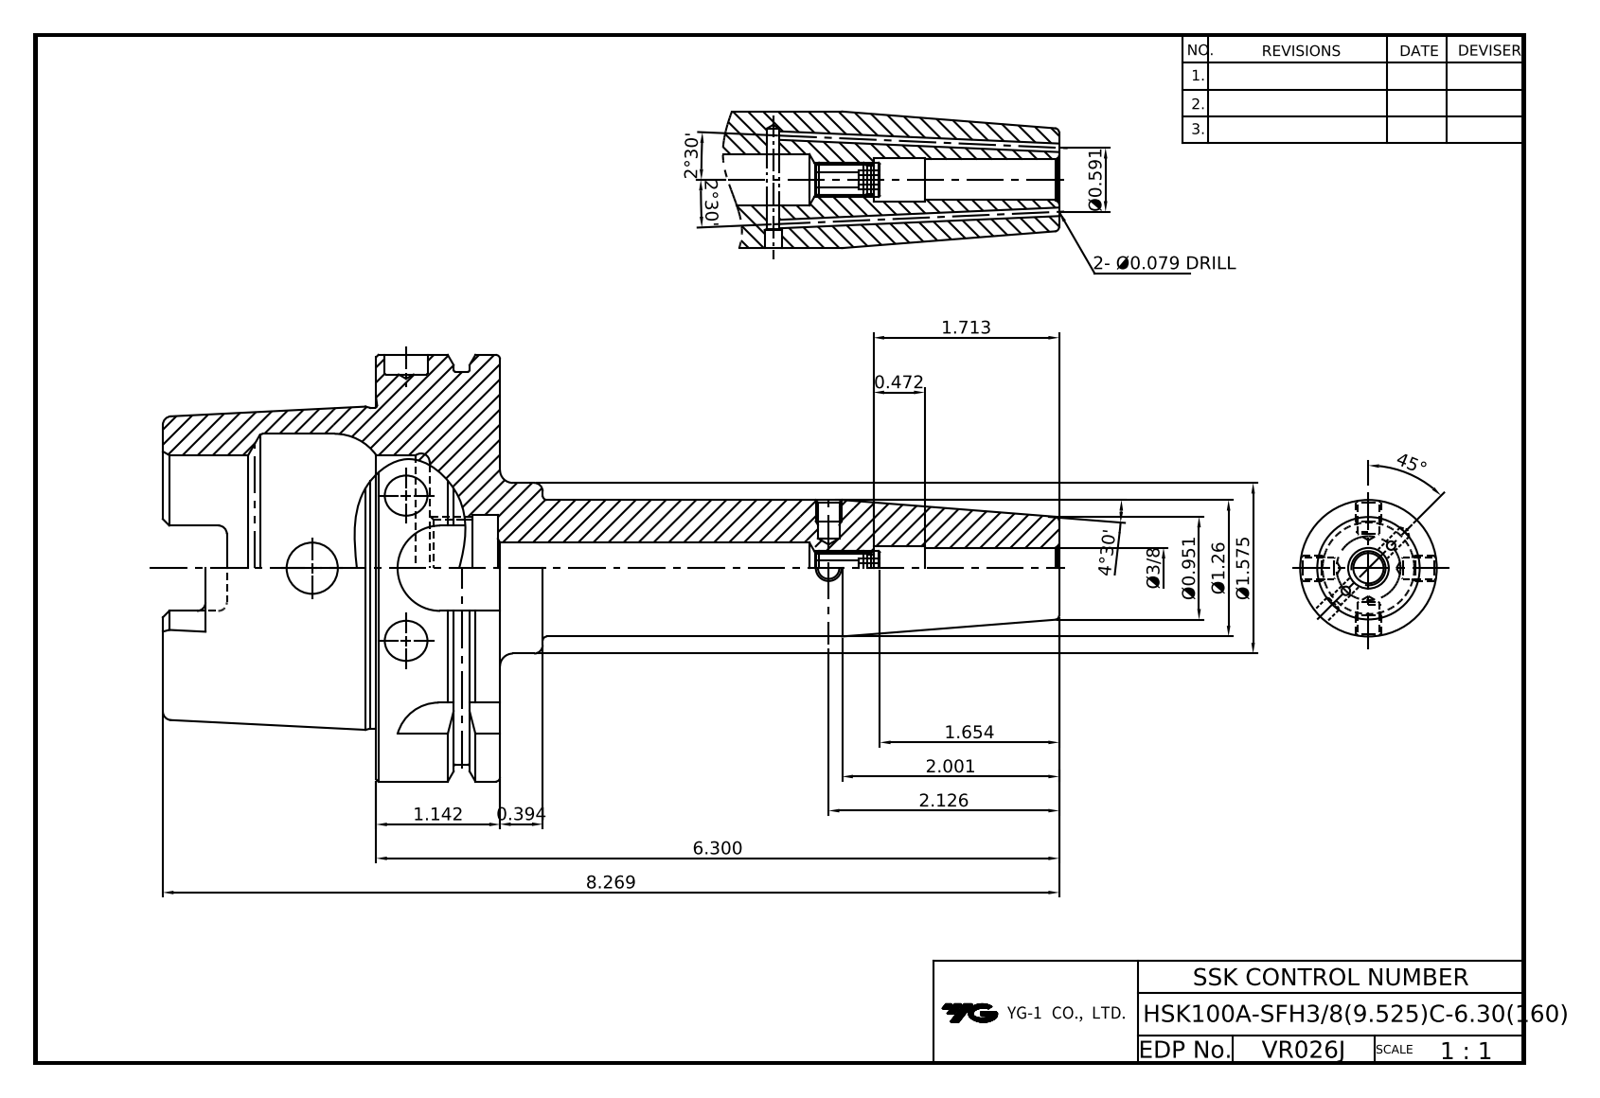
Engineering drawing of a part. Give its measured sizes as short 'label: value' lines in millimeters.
name: LO-HSK100A-SFH9.525C-160
written by: Autodesk Inventor 2022 (AUTOMOTIVE_DESIGN)
unit: mm
bodies: 1 solid, 121 faces (39 planar, 37 cylindrical, 45 other)
size: 210 × 100 × 100
volume: 347 789 mm³; area: 65 860 mm²
holes: 2× ⌀2, 1× ⌀6.92, 1× ⌀9.53, 1× ⌀10, 1× ⌀10.73, 1× ⌀12, 1× ⌀22.38, 1× ⌀25, 1× ⌀53, 1× ⌀63
bosses: 1× ⌀100, 1× ⌀92, 1× ⌀75.41, 1× ⌀40, 1× ⌀32
rounds: 6× R2, 4× R4.88, 4× R10
face distances: 29, 12.5, 16.5, 79, 62.5, 50, 88, 78.5, 28.5, 16
